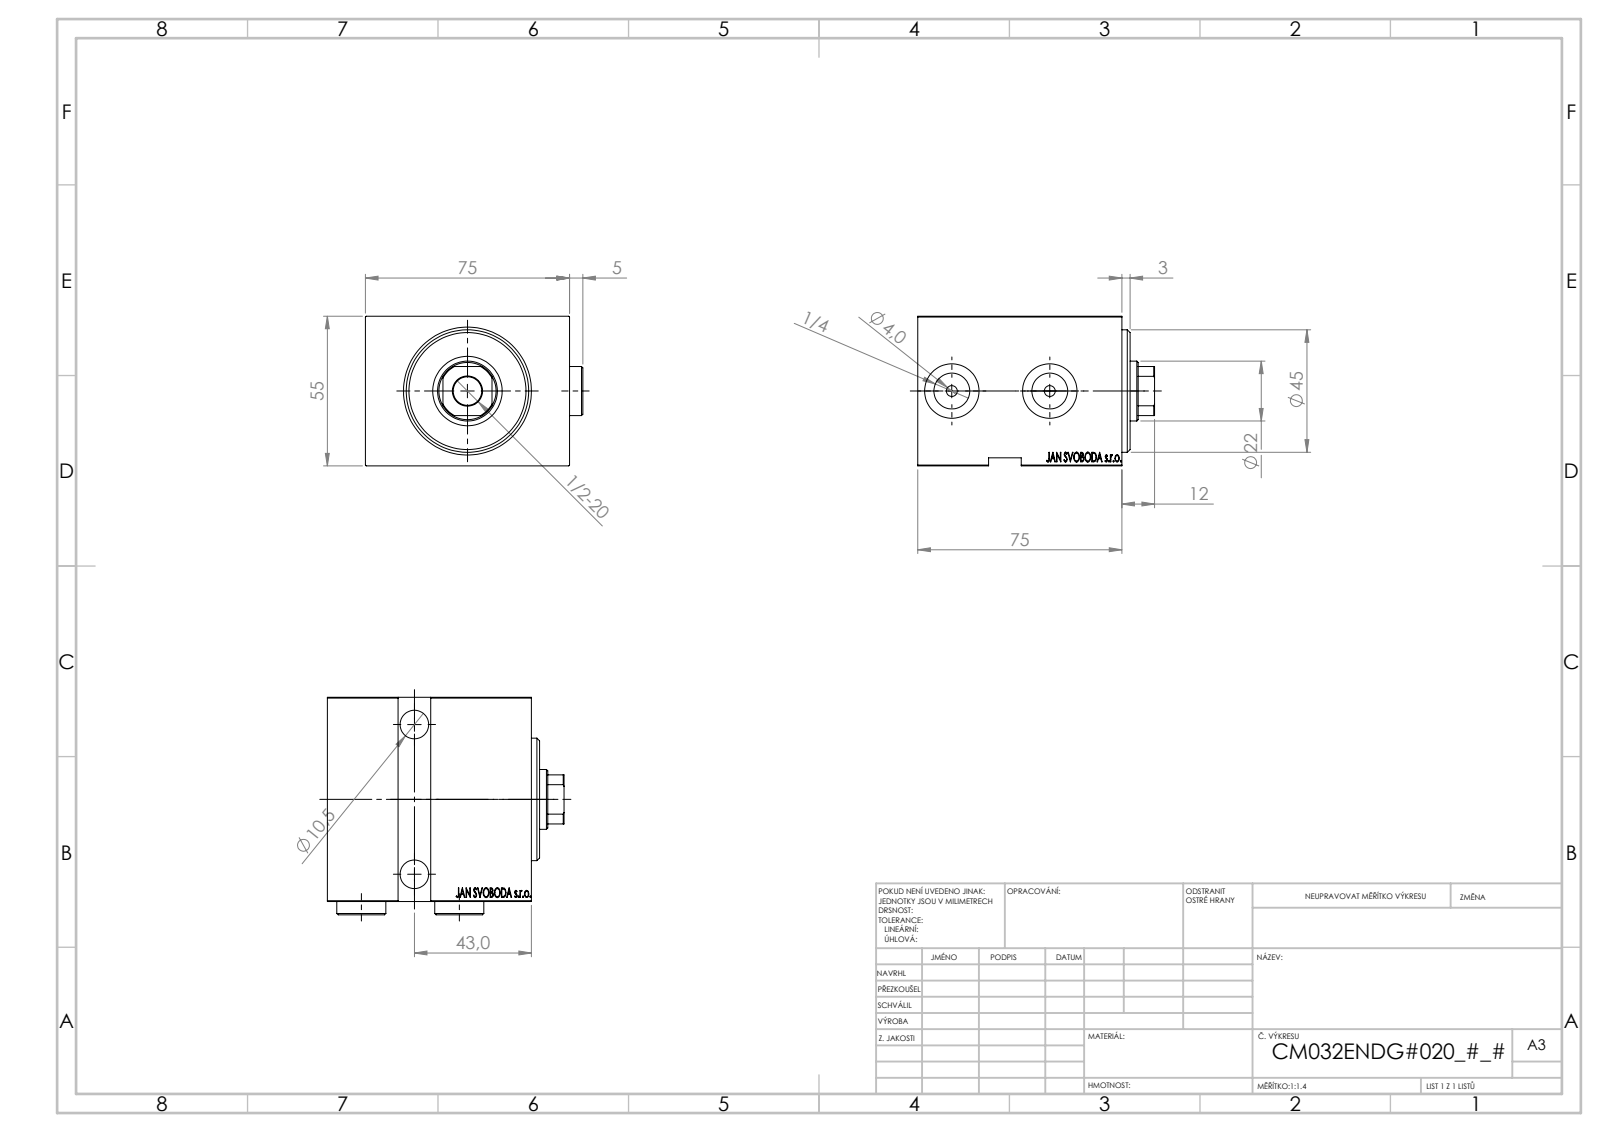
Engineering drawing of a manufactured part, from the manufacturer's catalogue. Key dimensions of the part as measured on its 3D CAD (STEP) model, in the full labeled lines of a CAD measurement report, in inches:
Part name (STEP PRODUCT): V450CM_E_Body; Zatka_OIL_PORT; V450CM_E_VCP; V450CM_VC_B
STEP written by: SolidWorks 2019 (CONFIG_CONTROL_DESIGN)
Units: inches
Bodies: 5 solids, 899 faces (443 planar, 58 cylindrical, 398 other)
Overall size (bounding box): 3.425 × 3.146 × 2.165
Volume: 17.38 in³ · Surface area: 86.78 in²
Round holes (diameter × count): ⌀0.413 ×3, ⌀0.157 ×2, ⌀0.518 ×2, ⌀0.65 ×2, ⌀0.787 ×2, ⌀0.866 ×1, ⌀1.004 ×1, ⌀1.26 ×1, ⌀1.772 ×1
Round bosses / shafts (diameter × count): ⌀0.709 ×2, ⌀1.339 ×1
Partial cylindrical surfaces — rounded edges, fillets, slot ends (radius × count): R0.413 ×1
Main face-to-face distances: 2.953, 2.165, 0.197, 0.118, 2.559, 0.394, 2.756, 2.362, 2.949, 0.472
Hole centre spacings: 1.417, 2.165
